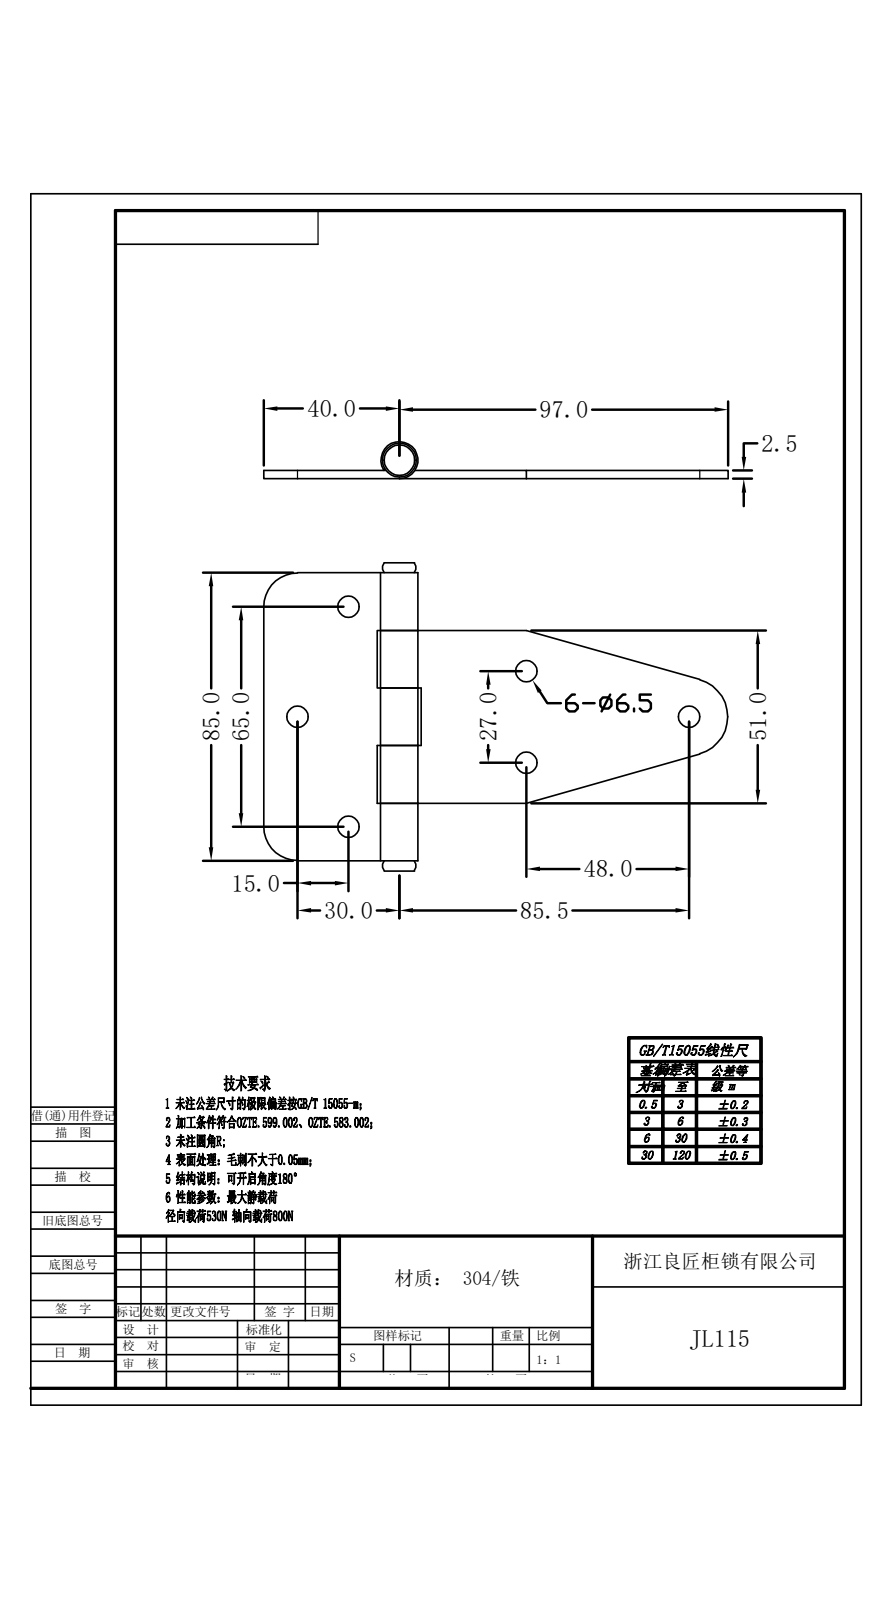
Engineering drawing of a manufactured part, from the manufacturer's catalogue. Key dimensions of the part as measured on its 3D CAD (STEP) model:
STEP written by: Rhino 8.5 (CONFIG_CONTROL_DESIGN)
Units: millimetres
Bodies: 3 solids, 64 faces (30 planar, 25 cylindrical, 9 other)
Overall size (bounding box): 137 × 93 × 11
Volume: 25 729 mm³ · Surface area: 22 417 mm²
Round holes (diameter × count): ⌀6.5 ×6, ⌀6 ×1
Round bosses / shafts (diameter × count): ⌀11 ×1, ⌀5.7 ×1
Partial cylindrical surfaces — rounded edges, fillets, slot ends (radius × count): R10 ×2
Main face-to-face distances: 2.5, 17, 51, 68, 34, 85, 34.67, 4, 21, 38
Hole centre spacings: 35.79, 49.16, 56.52, 69.55, 70.35, 105.62, 27, 65
